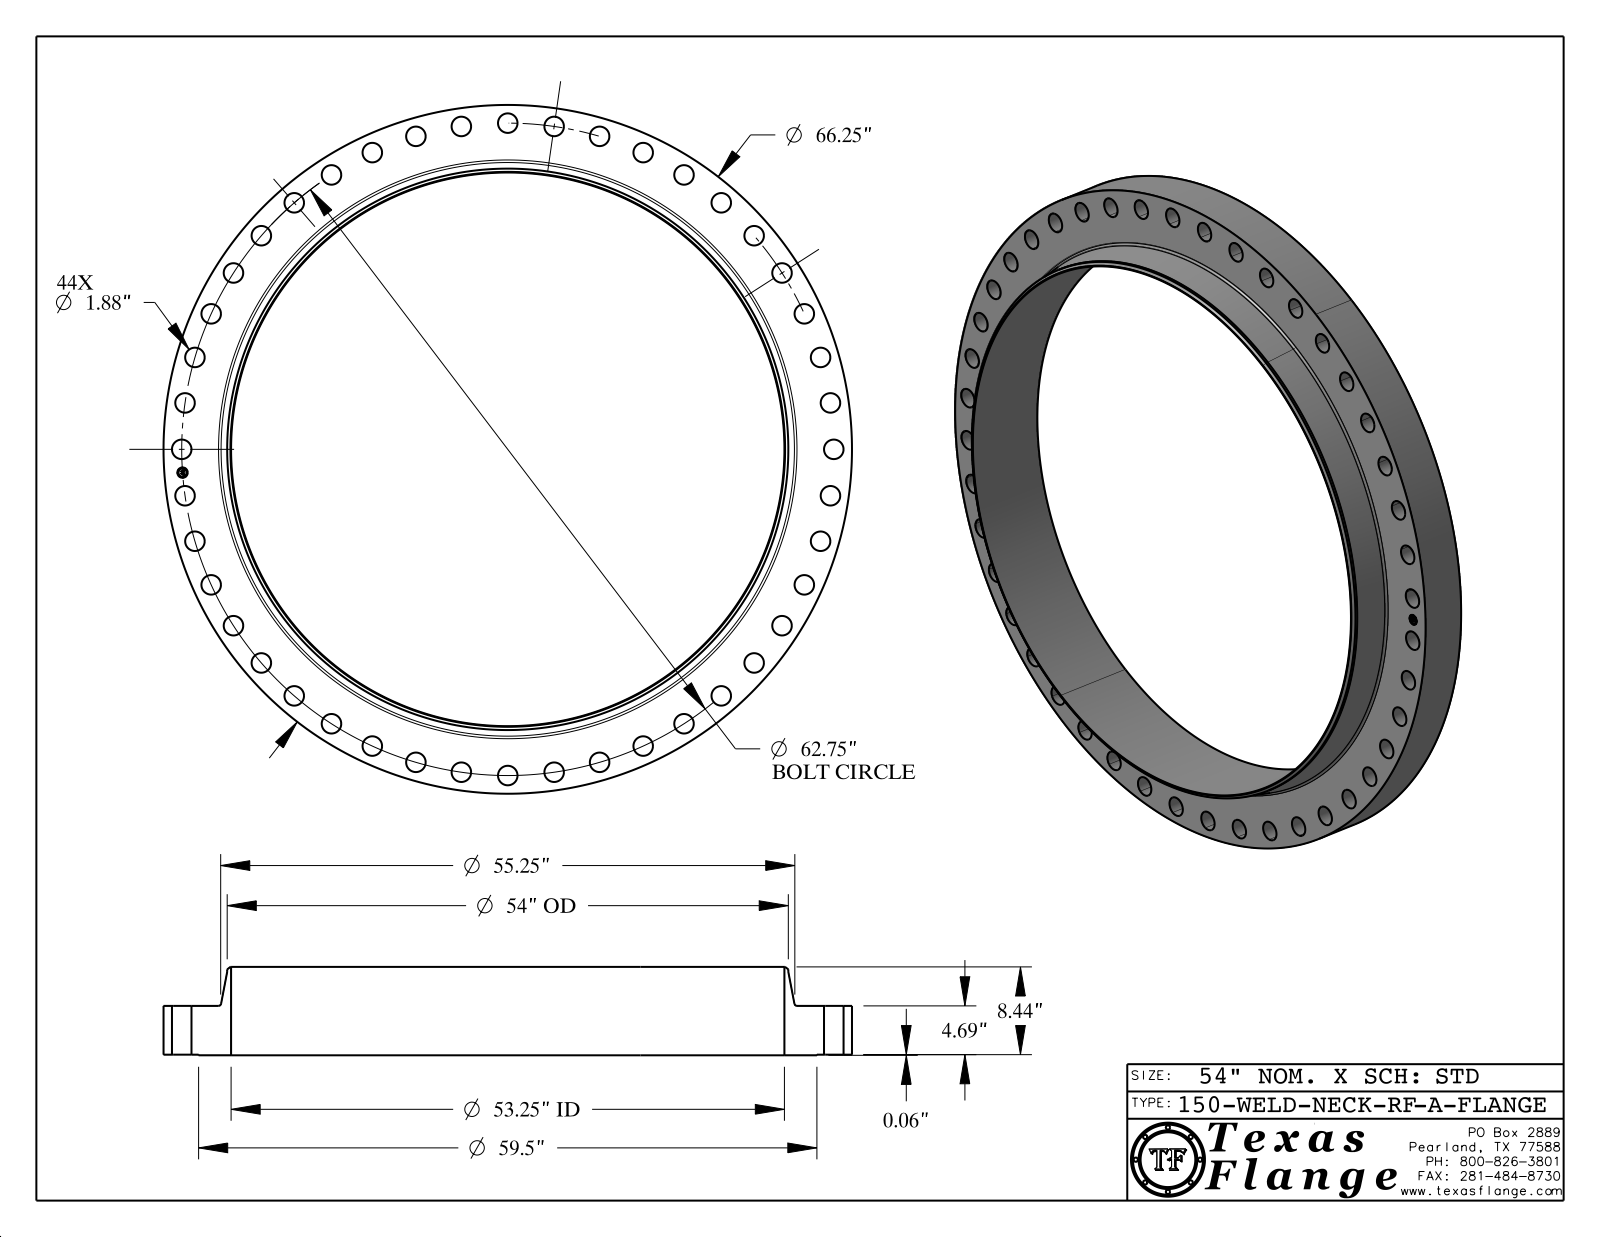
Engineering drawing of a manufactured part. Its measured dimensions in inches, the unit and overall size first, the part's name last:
Units: inches
Overall size (bounding box): 66.25 × 66.25 × 8.503
Round holes (diameter × count): ⌀1.88 ×44, ⌀1 ×1, ⌀53.25 ×1
Round bosses / shafts (diameter × count): ⌀0.061 ×8, ⌀66.25 ×1, ⌀59.5 ×1, ⌀54 ×1, ⌀0.788 ×1
Main face-to-face distances: 4.753, 0.063, 4.69, 8.503, 8.44, 3.75, 0.015, 4.738, 4.675, 3.765
Hole centre spacings: 62.59, 62.111, 31.375, 61.316, 4.476, 8.93, 21.929, 13.338
Volume: 5 591 in³ · Surface area: 6 332 in²
Bodies: 1 solid, 491 faces (369 planar, 116 cylindrical, 6 other)
Part name (STEP PRODUCT): 150-WELD-NECK-RF, Series A
STEP written by: CATIA V5 STEP AP214 (AUTOMOTIVE_DESIGN)
